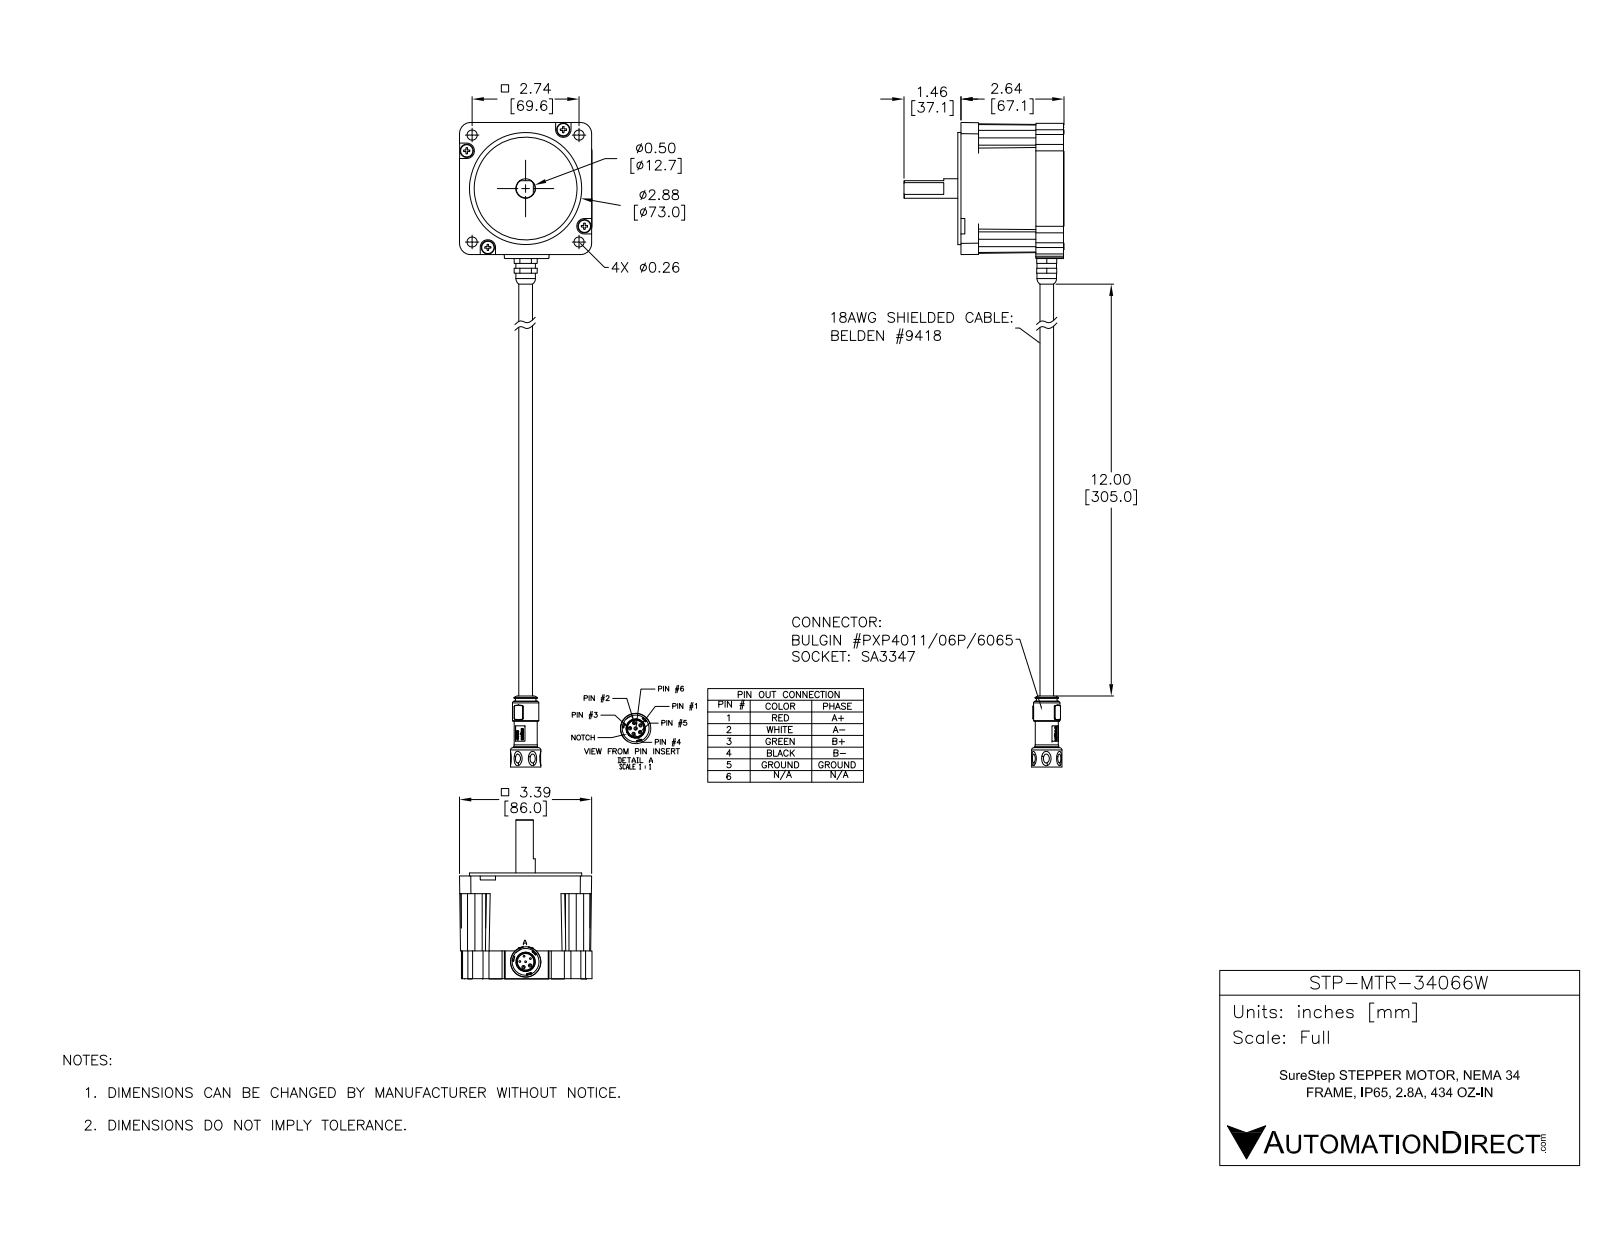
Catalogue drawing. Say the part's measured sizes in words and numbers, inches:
The part is named "STP-MTR-34066W". Its 3-D file was written by "SolidWorks 2017 (AUTOMOTIVE_DESIGN)". It is 3 solids with 837 faces: 308 planar, 234 cylindrical and 295 other. Overall it measures 16.516 by 4.08 by 3.386 inches. Its volume is 29.04 cubic inches and its surface area 83.68 square inches. Round holes: 6 of diameter 0.047, 4 of diameter 0.13, 4 of diameter 0.26, 1 of diameter 0.125, 1 of diameter 0.228, 1 of diameter 0.449, 1 of diameter 0.689, 1 of diameter 0.75, 1 of diameter 2.638. Round bosses or shafts: 4 of diameter 0.05, 2 of diameter 0.5, 1 of diameter 3.125, 1 of diameter 2.875, 1 of diameter 0.777, 1 of diameter 0.674, 1 of diameter 0.613, 1 of diameter 0.592. Partial cylindrical surfaces (rounded edges, fillets, slot ends): 28 of radius 0.005, 16 of radius 0.008, 14 of radius 0.02, 8 of radius 0.188, 6 of radius 0.388, 4 of radius 0.187, 4 of radius 0.197, 3 of radius 0.287. The main face-to-face distances are 2.68, 0.04, 2.64, 2.63, 2.67, 3.346, 2.222, 2.21, 2.2, 0.43. The hole center spacings are 0.148, 0.174, 0.147, 1.937, 2.533, 2.74, 0.281, 3.707.
